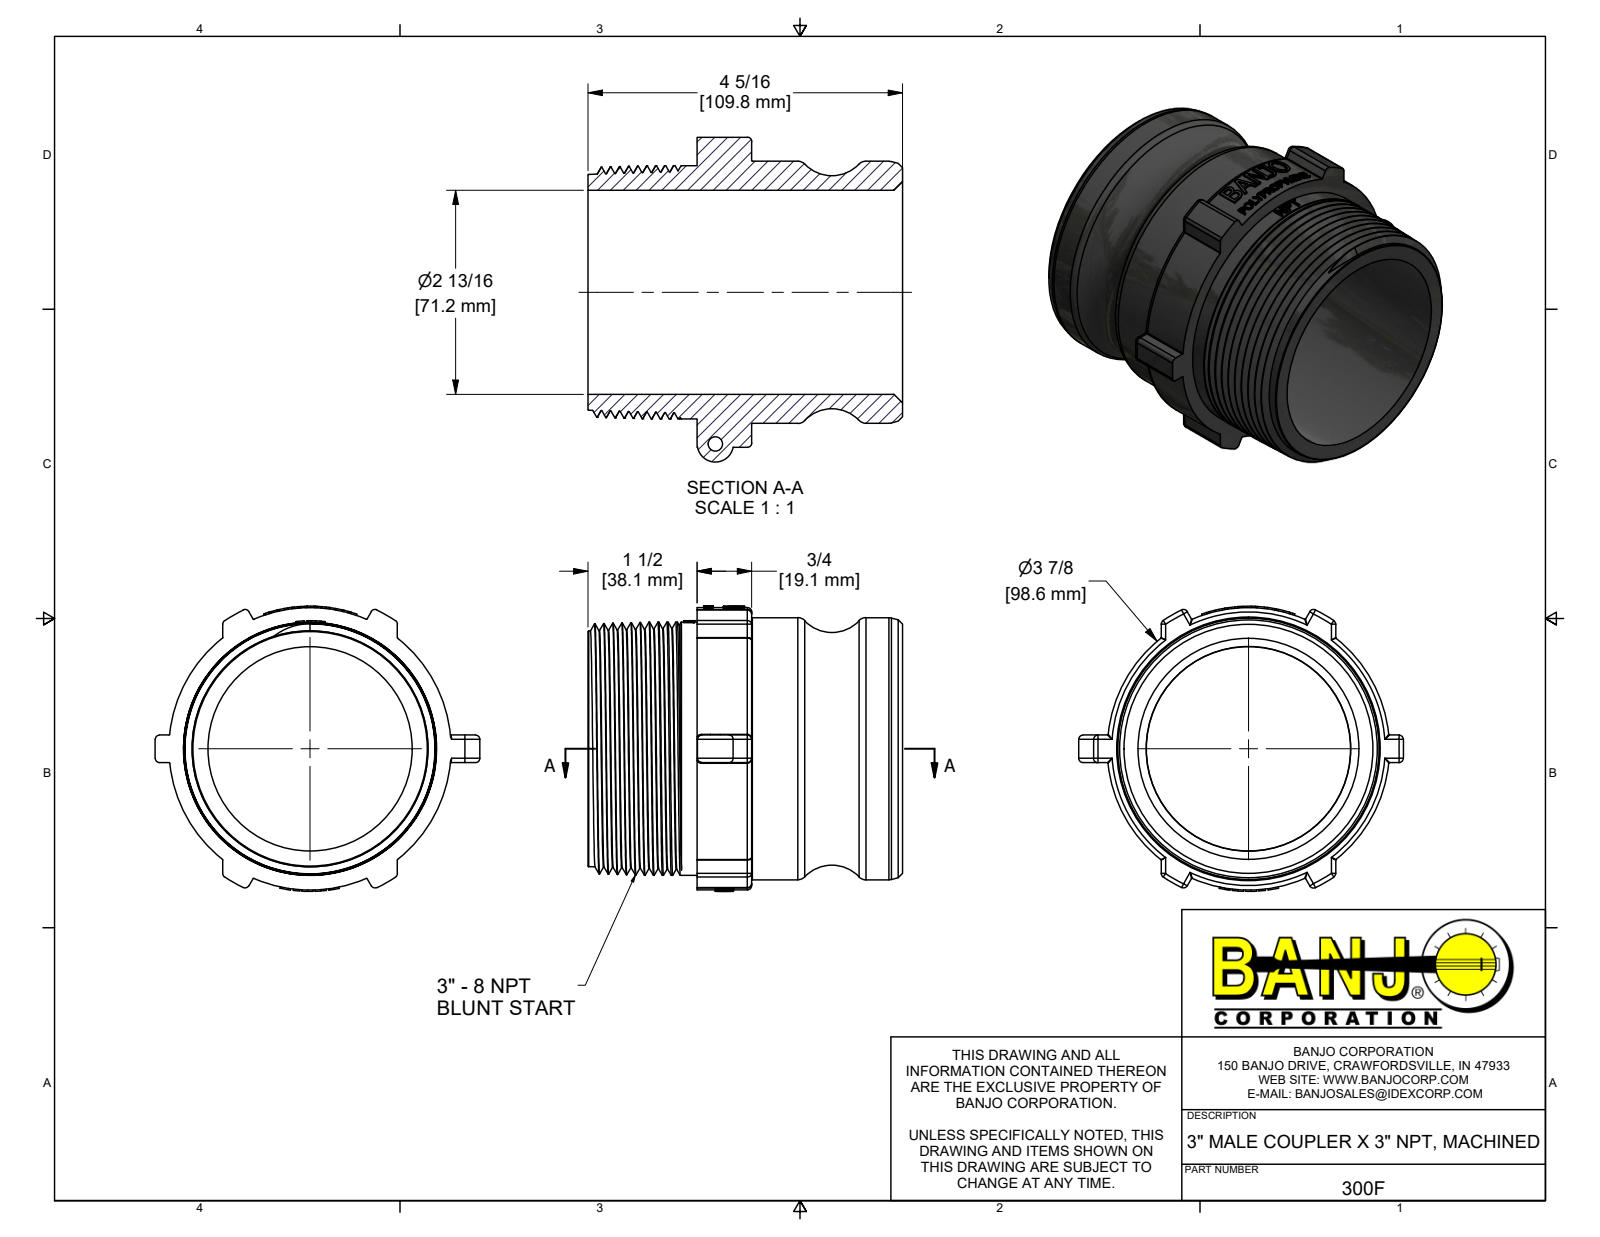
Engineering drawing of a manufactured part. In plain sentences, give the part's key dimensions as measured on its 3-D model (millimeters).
The part is named "300F; 300FX". Its 3-D file was written by "Autodesk Inventor 2019 (AUTOMOTIVE_DESIGN)". It is 1 solid with 513 faces: 183 planar, 99 cylindrical and 231 other. Overall it measures 1433.9 by 113 by 100.1 millimeters. Its volume is 252 000 cubic millimeters and its surface area 423 400 square millimeters. Round holes: 1 of diameter 5.1, 1 of diameter 71.9. Round bosses or shafts: 1 of diameter 91.5, 1 of diameter 88.9. Partial cylindrical surfaces (rounded edges, fillets, slot ends): 24 of radius 1.5, 12 of radius 0.3, 1 of radius 6.4, 1 of radius 20.5, 1 of radius 45, 1 of radius 49.5, 1 of radius 50, 1 of radius 53.3. The main face-to-face distances are 71.7, 109.8, 38.1, 52.7, 19.1, 57.2, 22.9, 83.8, 61, 10.3.
